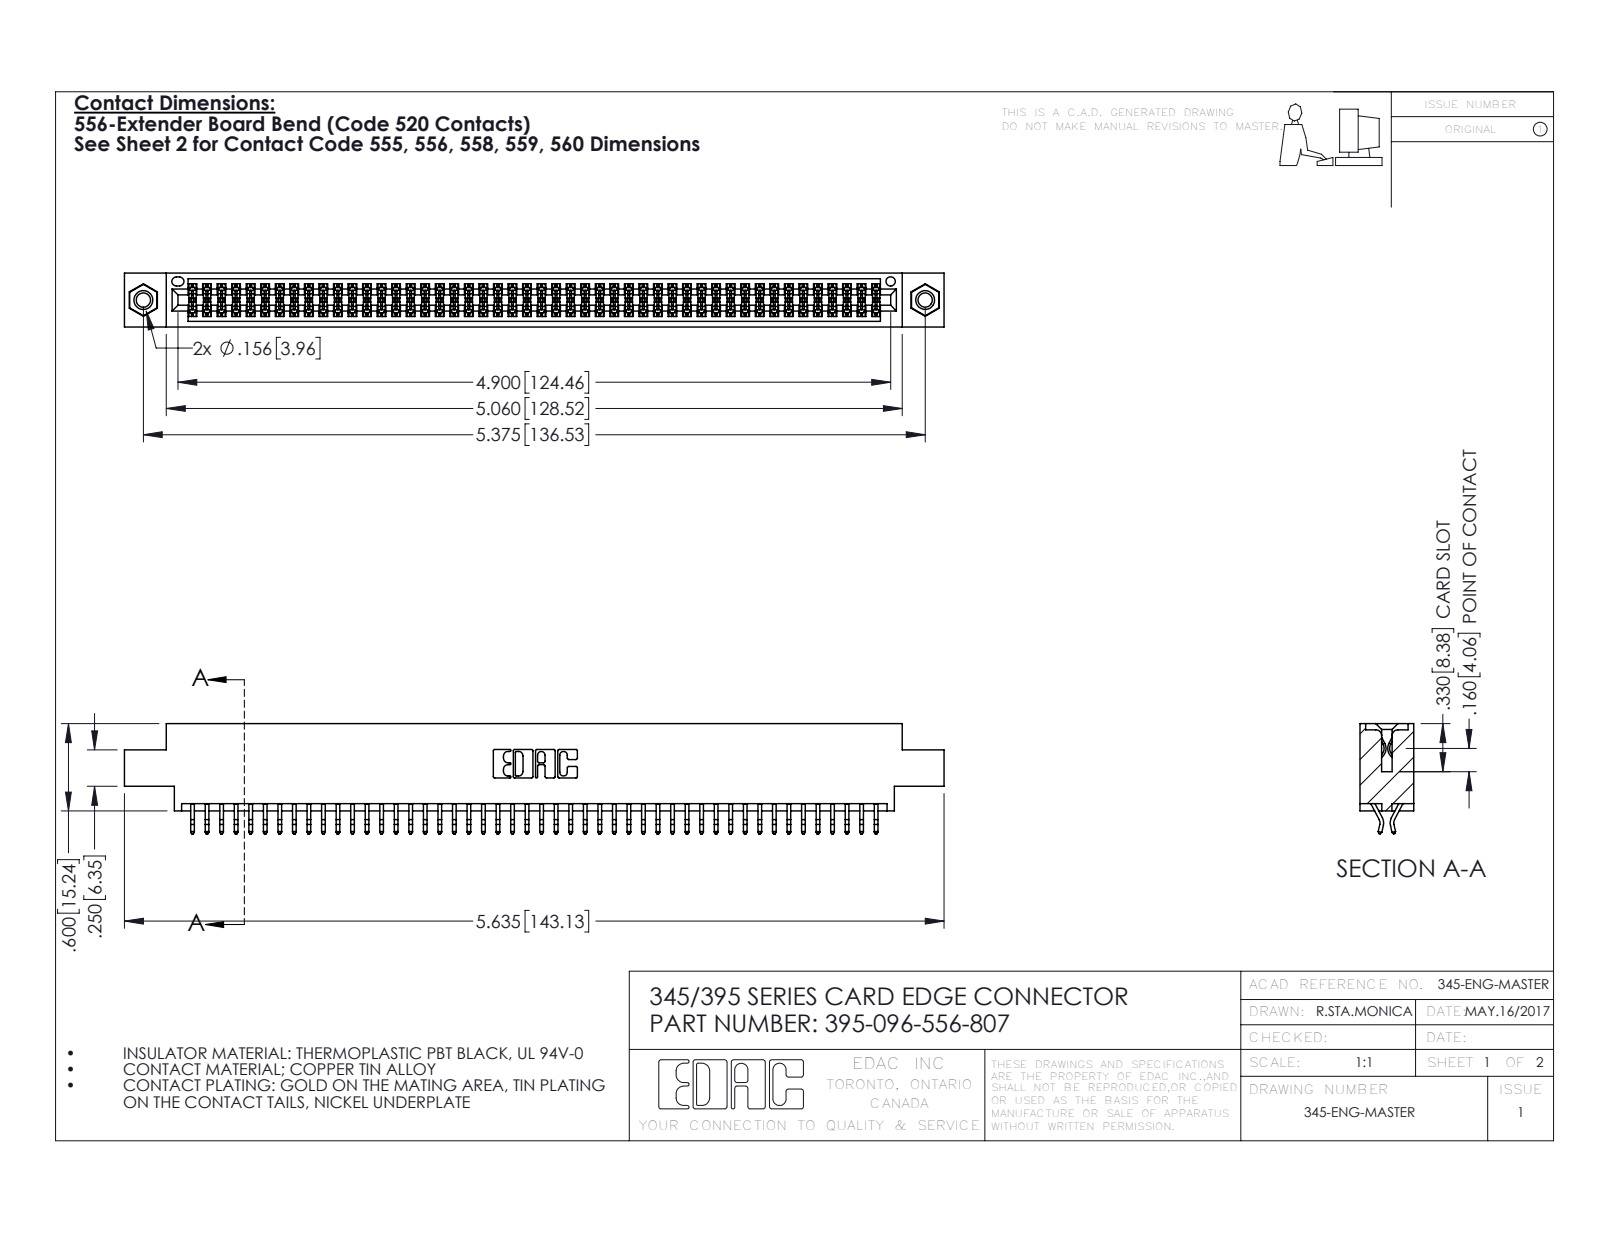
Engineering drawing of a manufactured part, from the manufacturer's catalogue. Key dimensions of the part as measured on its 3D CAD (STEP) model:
Part name (STEP PRODUCT): 395-096-556-807; 345-250-001_345-250-005-103; 345-292-001_556 Tail; 345 Part_0.170 Offset - 0.156 Dia-TI
STEP written by: SolidWorks 2016 (CONFIG_CONTROL_DESIGN)
Units: inches
Bodies: 99 solids, 5566 faces (3668 planar, 1882 cylindrical, 16 other)
Overall size (bounding box): 5.635 × 0.757 × 0.37
Volume: 0.844 in³ · Surface area: 32 in²
Round holes (diameter × count): ⌀0.098 ×2, ⌀0.125 ×2, ⌀0.156 ×2, ⌀0.064 ×1
Round bosses / shafts (diameter × count): ⌀0.155 ×2
Partial cylindrical surfaces — rounded edges, fillets, slot ends (radius × count): R0.006 ×144, R0.01 ×22, R0.007 ×6, R0.031 ×6, R0.026 ×3, R0.01 ×2, R0.014 ×2, R0.019 ×2
Main face-to-face distances: 0.072, 0.298, 0.37, 0.2, 0.025, 0.098, 0.272, 0.225, 0.175, 0.149
Hole centre spacings: 0.27, 5.139, 5.375
